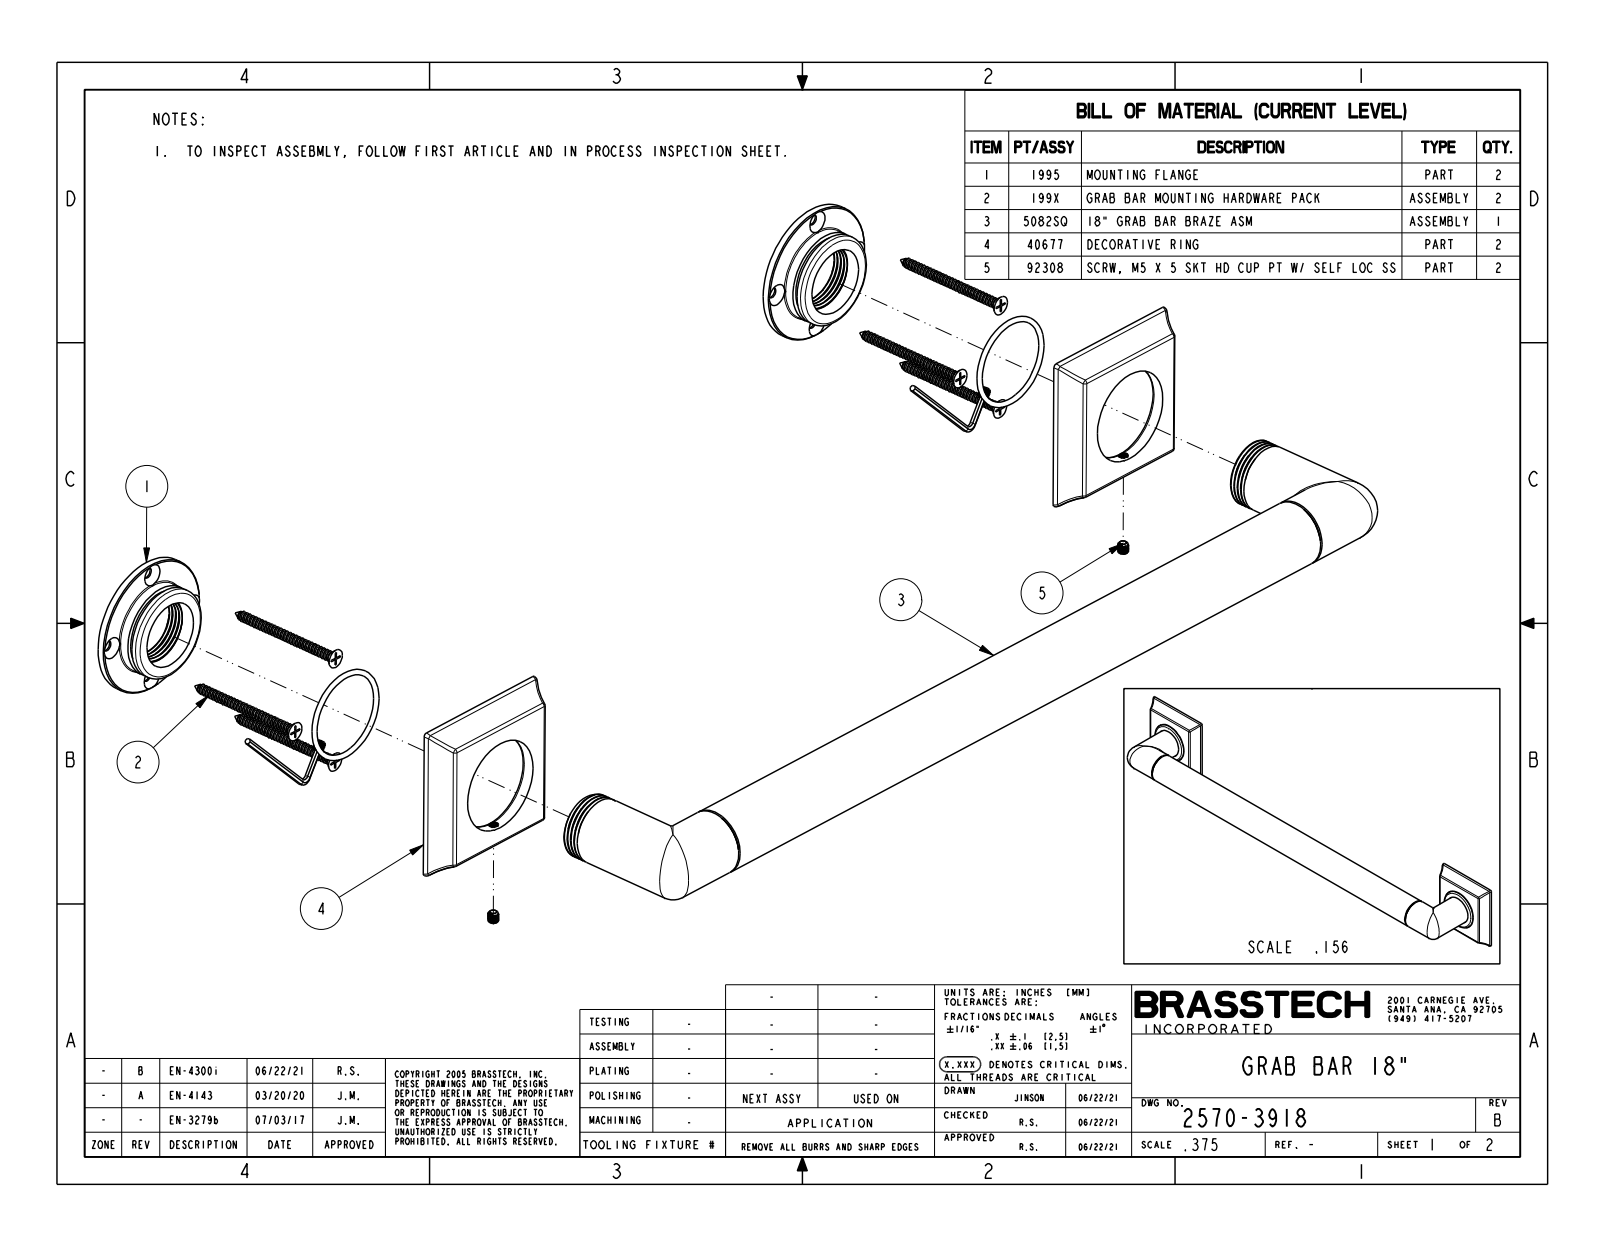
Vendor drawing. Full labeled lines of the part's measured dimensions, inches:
Part name (STEP PRODUCT): 2570-3918
STEP written by: CREO PARAMETRIC BY PTC INC, 2018400 (CONFIG_CONTROL_DESIGN)
Units: inches
Bodies: 1 solid, 88 faces (6 planar, 38 cylindrical, 44 other)
Overall size (bounding box): 21 × 3 × 2.755
Volume: 33.86 in³ · Surface area: 123.2 in²
Round bosses / shafts (diameter × count): ⌀1.25 ×3, ⌀1.75 ×2
Partial cylindrical surfaces — rounded edges, fillets, slot ends (radius × count): R0.06 ×6, R0.125 ×6, R1.35 ×6
Main face-to-face distances: 0.525, 0.6, 0.075
